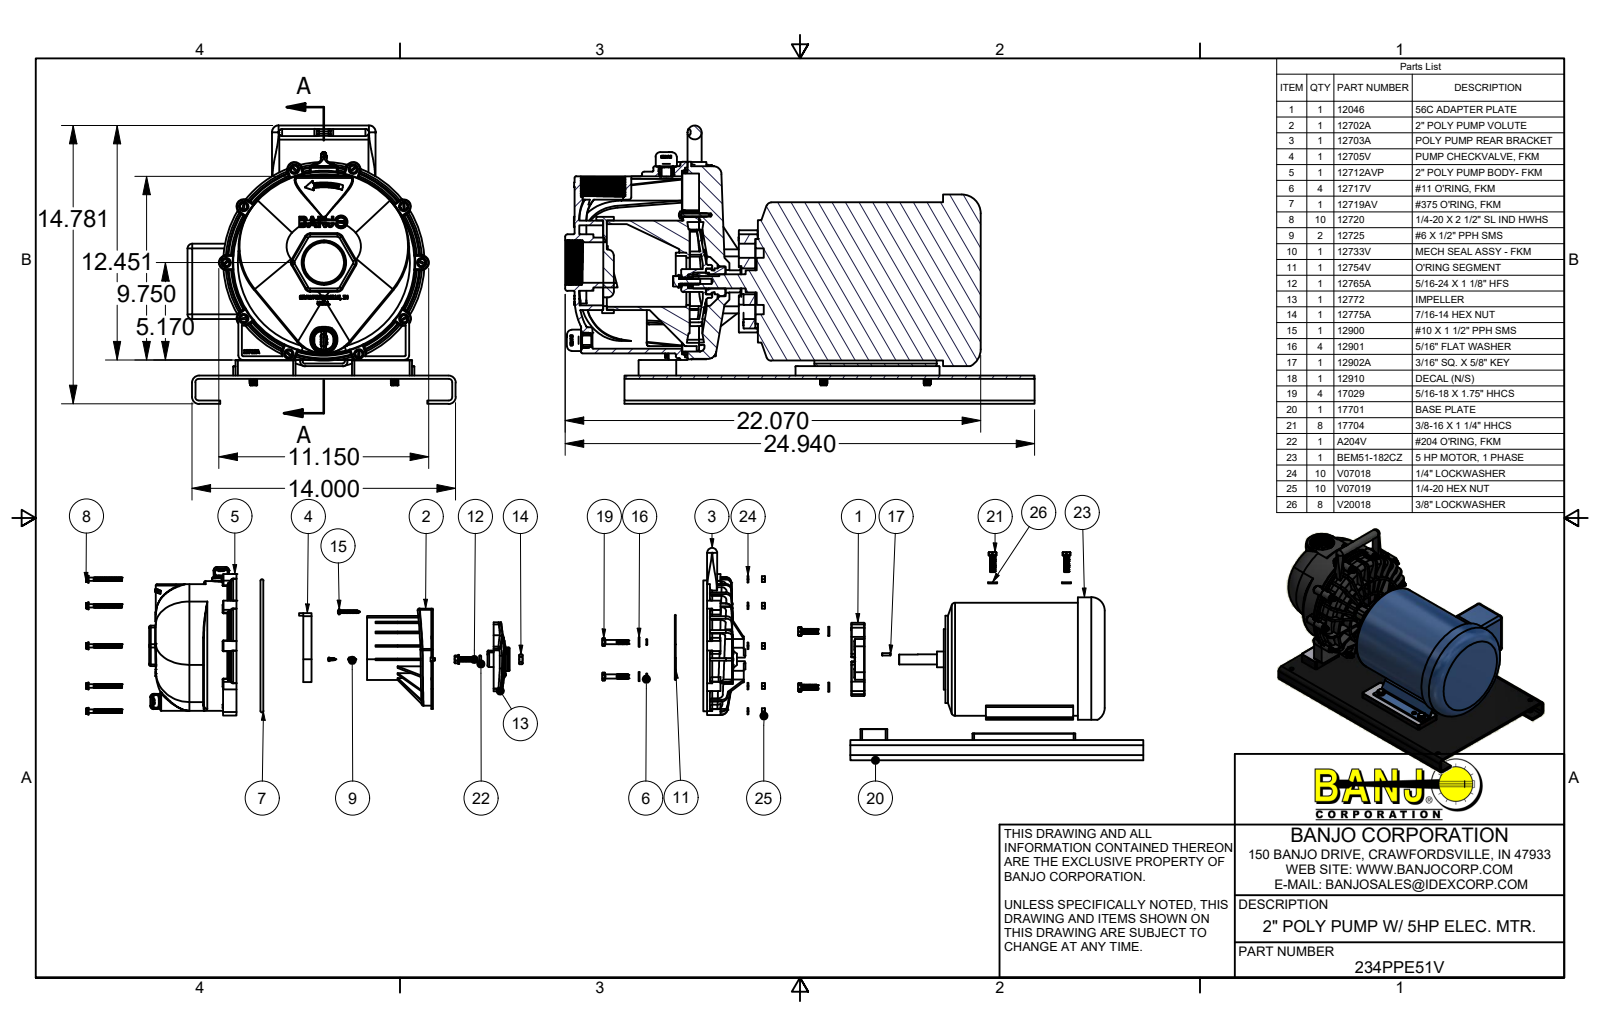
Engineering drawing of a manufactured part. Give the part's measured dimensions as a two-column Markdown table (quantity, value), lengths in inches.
| quantity | value |
| --- | --- |
| part name | 234PPE51V; 12703A; 12046; 12046X (+8 more) |
| STEP written by | Autodesk Inventor 2019 (AUTOMOTIVE_DESIGN) |
| units | inches |
| bodies | 107 solids, 11146 faces (3002 planar, 3221 cylindrical, 4923 other) |
| overall size | 24.94 × 14.781 × 14.24 |
| volume | 1 006 in³ |
| surface area | 3 335 in² |
| round holes (diameter × count) | 0.307 × 16, 0.252 × 14, 0.196 × 10, 0.27 × 10, 0.41 × 10, 0.385 × 8, 0.22 × 7, 0.5 × 6, 0.344 × 4, 0.359 × 4, 0.401 × 4, 0.406 × 4 |
| round bosses / shafts (diameter × count) | 0.324 × 152, 0.268 × 60, 0.52 × 10, 0.489 × 10, 0.25 × 10, 0.687 × 8, 0.375 × 8, 0.192 × 6 |
| partial cylindrical surfaces (radius × count) | 0.03 × 166, 0.25 × 65, 0.125 × 47, 0.5 × 29, 0.06 × 27, 0.008 × 26, 0.187 × 24, 0.162 × 16 |
| main face-to-face distances | 0.18, 0.5, 2, 0.179, 0.68, 1.5, 1.321, 1.32, 1.141, 1.821 |
| hole center spacings | 2.561, 3.452, 5.2, 1, 1.125, 1.128, 2.615, 2.937 |
